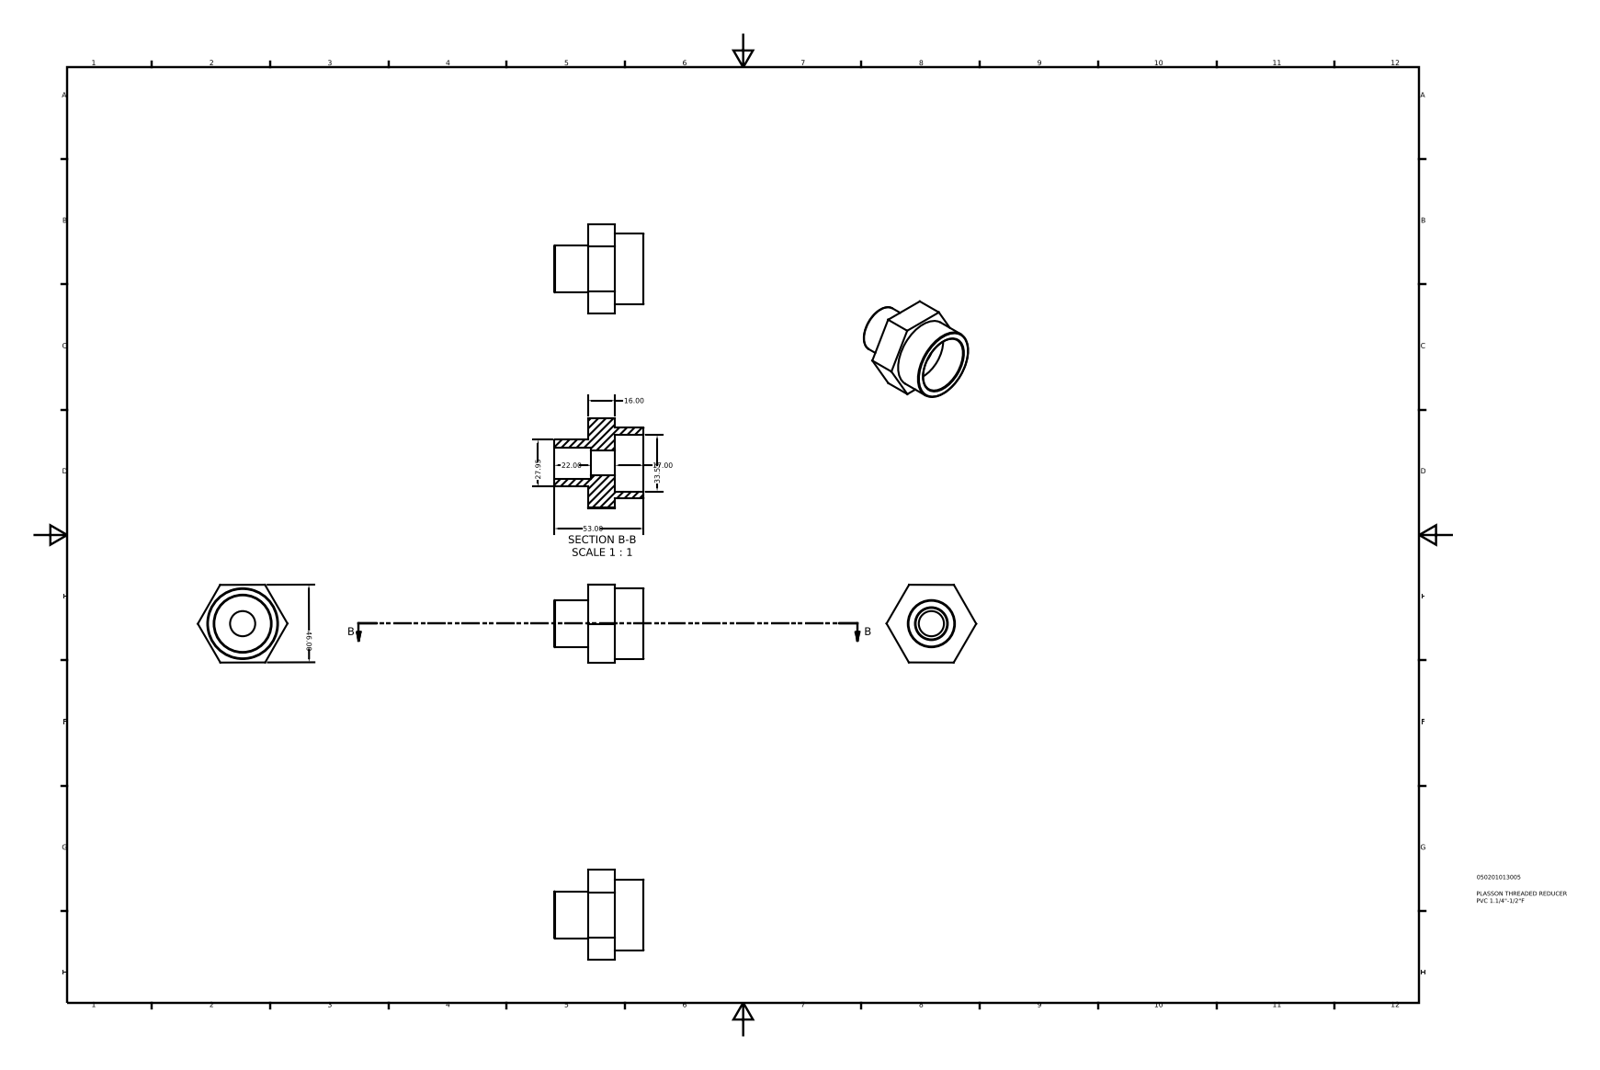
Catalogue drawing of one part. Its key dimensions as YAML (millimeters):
part_name: "050201013005"
step_written_by: "Autodesk Inventor 2015 (AUTOMOTIVE_DESIGN)"
units: millimeters
bodies: {solids: 1, faces: 21, planar: 12, cylindrical: 5, other: 4}
overall_size: [53.12, 53, 46.08]
volume: 41576
surface_area: 13525
round_holes:
  - {diameter: 14.9, count: 1}
  - {diameter: 18.63, count: 1}
  - {diameter: 33.53, count: 1}
round_bosses_or_shafts:
  - {diameter: 41.91, count: 1}
  - {diameter: 27.95, count: 1}
face_to_face_distances: [16, 46.02, 46, 46.04, 33, 17, 20, 36, 53, 22]
